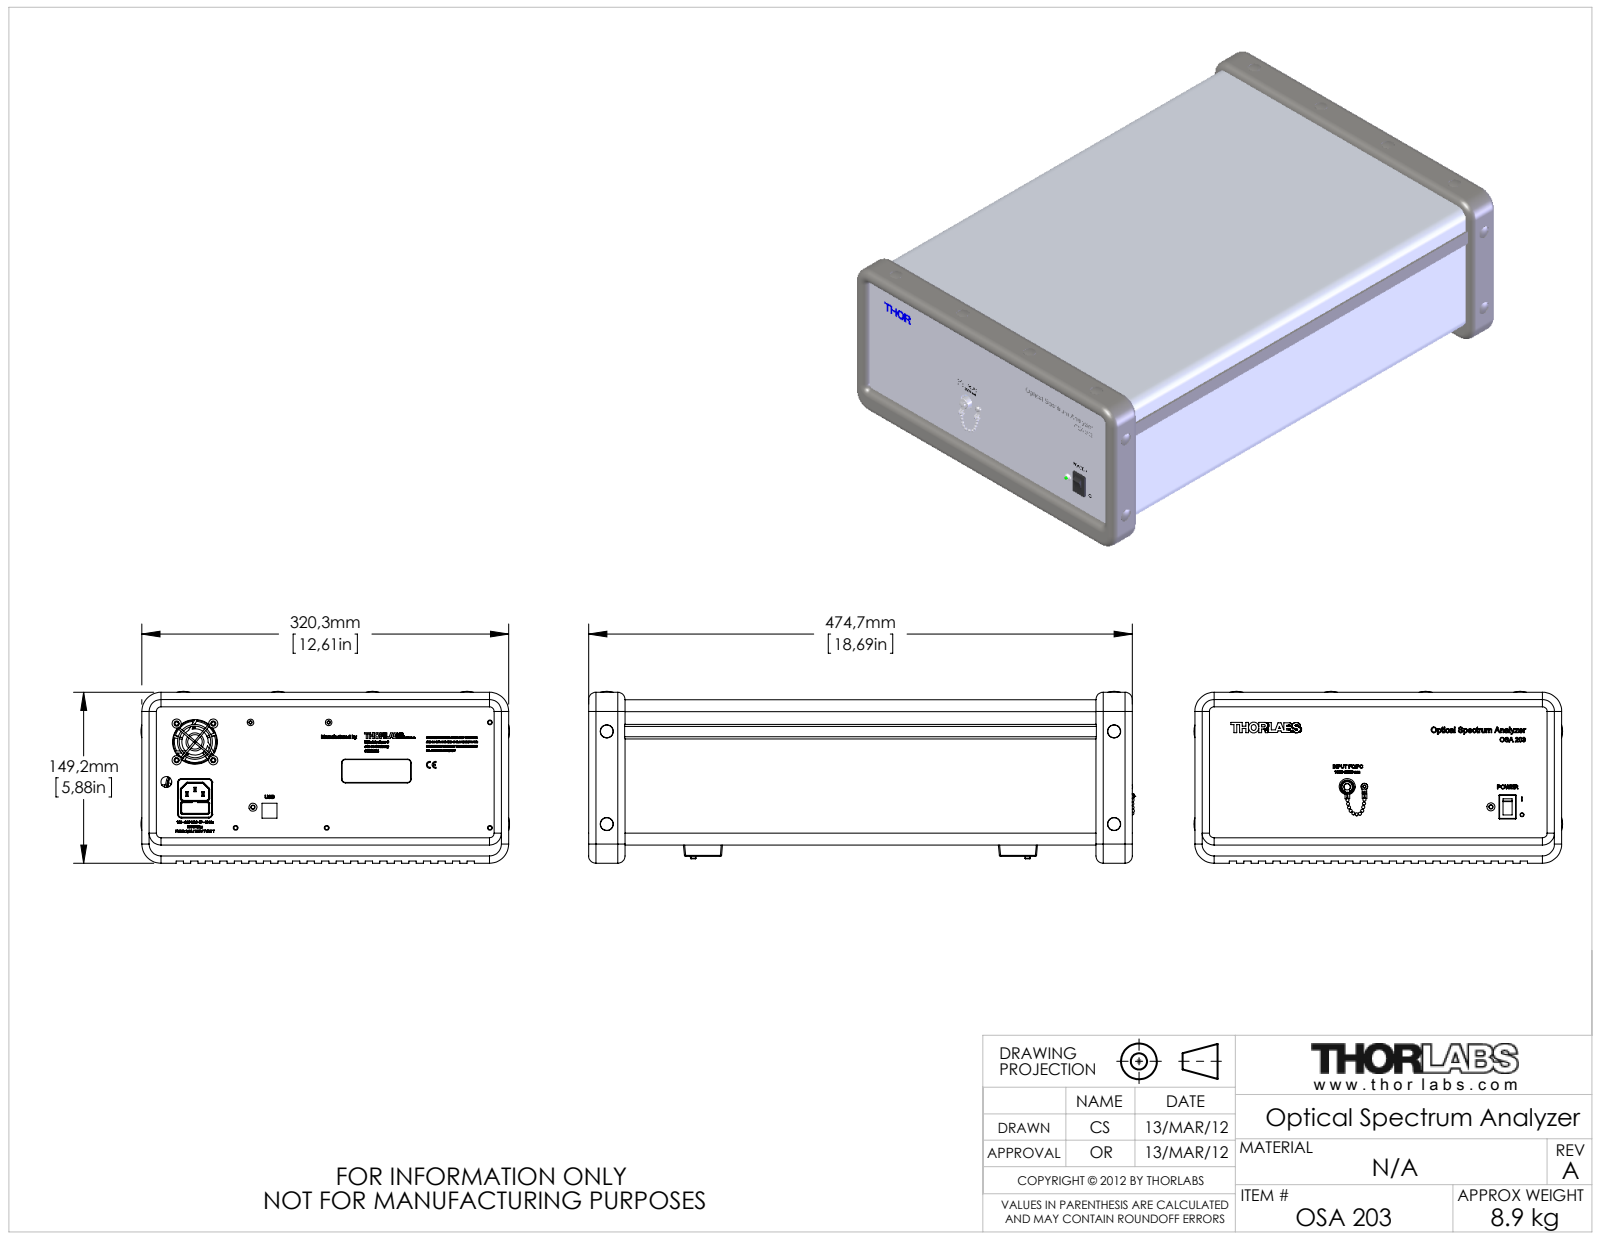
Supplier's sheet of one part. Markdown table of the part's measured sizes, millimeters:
| quantity | value |
| --- | --- |
| part name | 21146-E0W |
| STEP written by | SolidWorks 2011 (AUTOMOTIVE_DESIGN) |
| units | millimeters |
| bodies | 185 solids, 12607 faces (5536 planar, 4848 cylindrical, 2223 other) |
| overall size | 476.86 × 321.82 × 149.99 |
| volume | 1 811 000 mm³ |
| surface area | 1 745 000 mm² |
| round holes (diameter × count) | 2 × 704, 5.08 × 12, 11.43 × 12, 5.41 × 11, 0.94 × 10, 4.5 × 10, 2.26 × 9, 1.78 × 8, 3.1 × 8, 4.19 × 8, 4.22 × 8, 4.27 × 8 |
| round bosses / shafts (diameter × count) | 4 × 30, 5.02 × 17, 3 × 16, 8 × 12, 1.5 × 11, 11.05 × 10, 11.05 × 5, 12.5 × 4 |
| partial cylindrical surfaces (radius × count) | 0.5 × 124, 0.2 × 96, 0.3 × 78, 0.27 × 72, 0.91 × 72, 1 × 64, 0.79 × 48, 1.5 × 37 |
| main face-to-face distances | 1, 125.7, 124.7, 126.7, 306.6, 461, 15, 110.7, 81, 66 |
| hole center spacings | 11.18, 5, 15.81, 7.07, 10, 18.03, 15, 20.62 |
